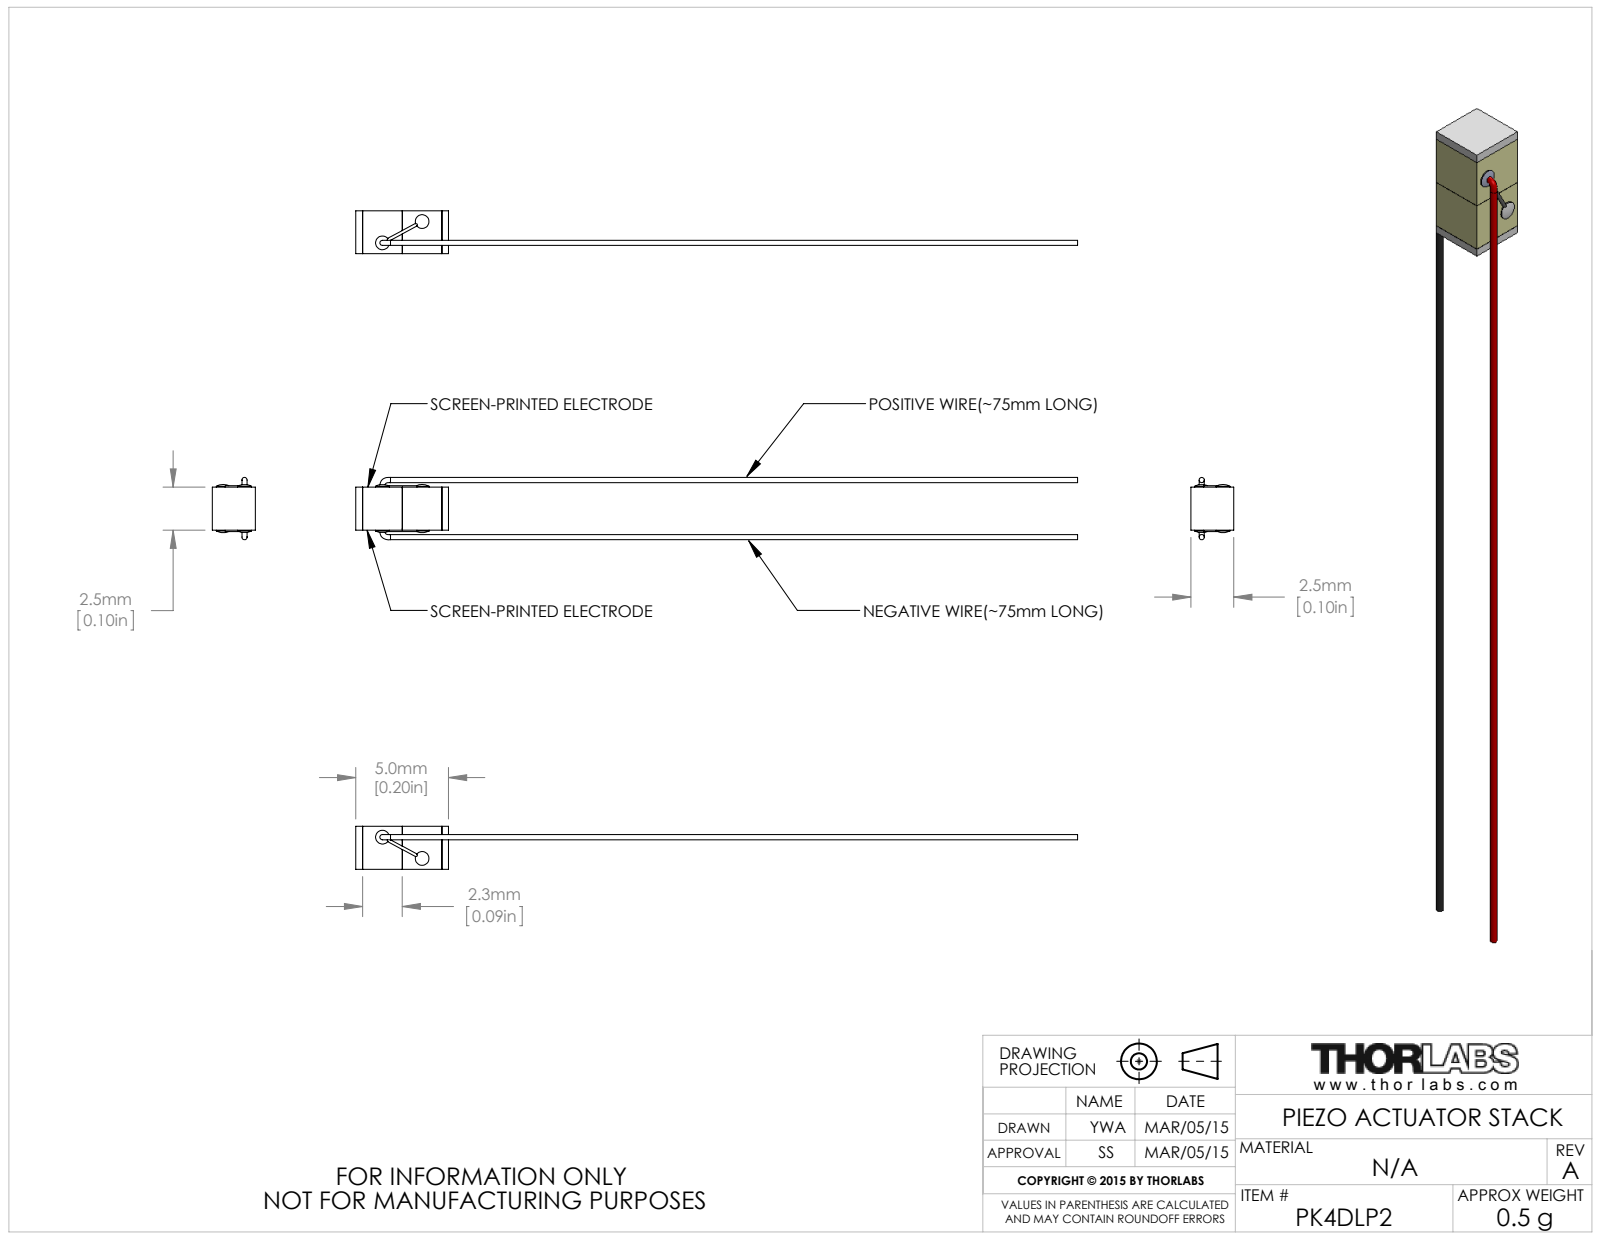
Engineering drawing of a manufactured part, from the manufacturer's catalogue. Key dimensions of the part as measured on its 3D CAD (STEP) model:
Part name (STEP PRODUCT): PK4DLP2
STEP written by: SolidWorks 2014 (AUTOMOTIVE_DESIGN)
Units: millimetres
Bodies: 3 solids, 58 faces (26 planar, 16 cylindrical, 16 other)
Overall size (bounding box): 42.02 × 3.63 × 2.5
Volume: 40 mm³ · Surface area: 182 mm²
Round bosses / shafts (diameter × count): ⌀0.8 ×2
Main face-to-face distances: 2.5, 2.31, 2.3, 0.37, 4.99, 5.39, 4.62, 5.02, 0.4, 0.38
